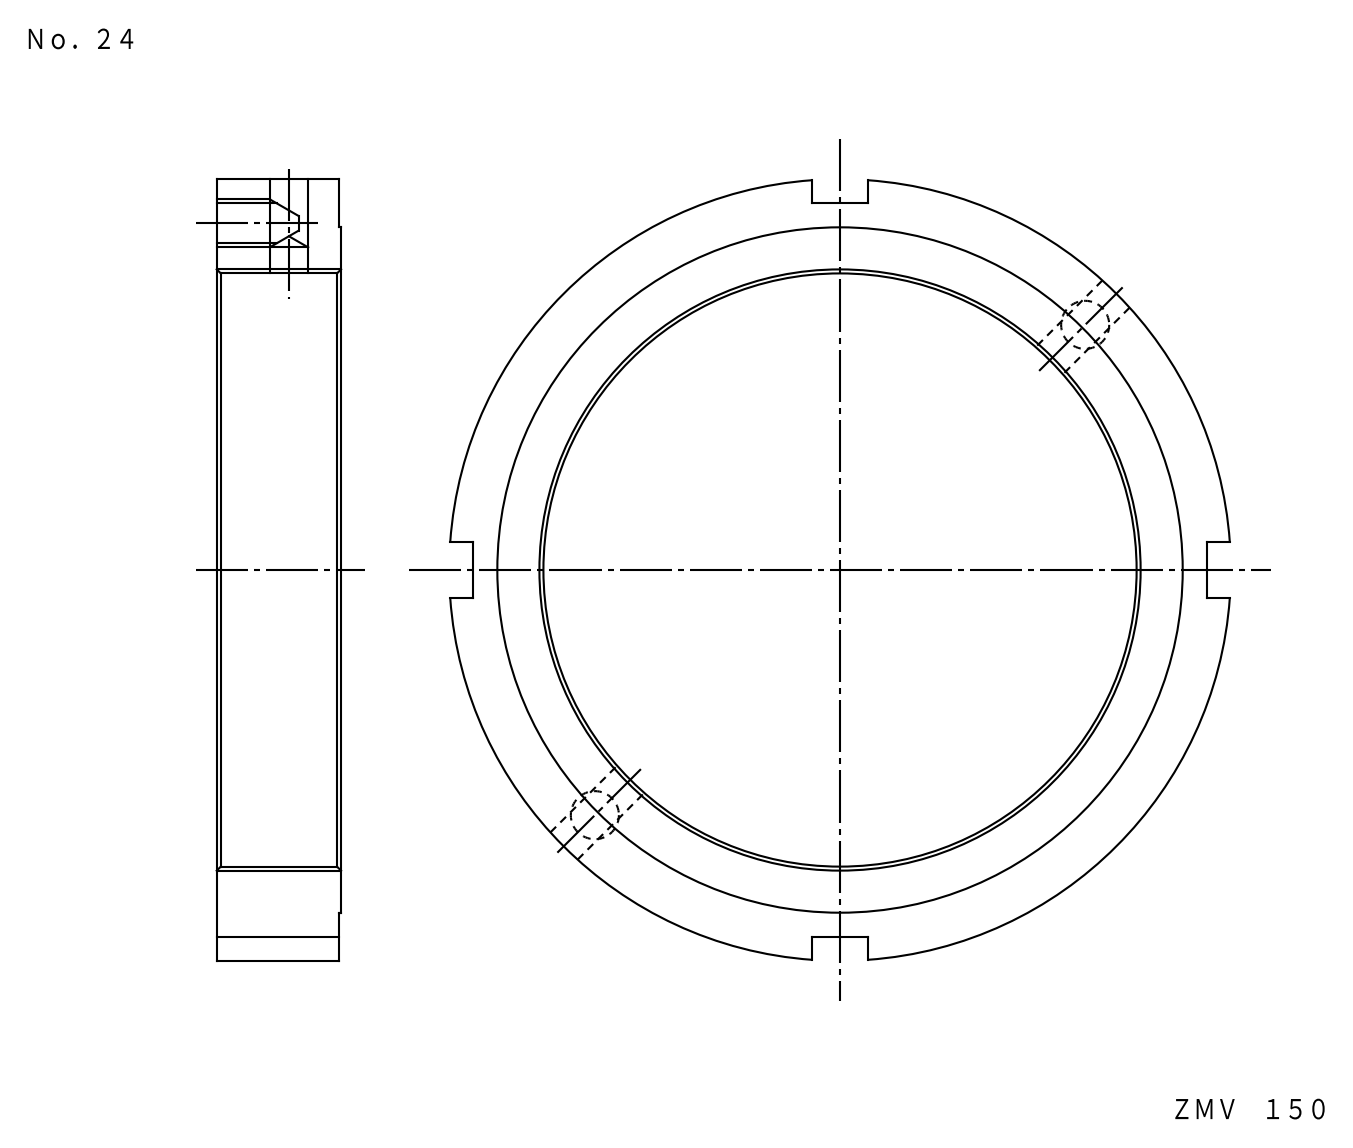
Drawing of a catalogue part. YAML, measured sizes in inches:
part_name: "FKD ZMV150"
step_written_by: "Autodesk Inventor LT (CONFIG_CONTROL_DESIGN)"
units: inches
bodies: {solids: 1, faces: 29, planar: 15, cylindrical: 10, other: 4}
overall_size: [7.657, 7.657, 1.22]
volume: 21.9
surface_area: 93.55
round_holes:
  - {diameter: 0.378, count: 2}
  - {diameter: 0.398, count: 2}
  - {diameter: 5.906, count: 1}
round_bosses_or_shafts:
  - {diameter: 7.677, count: 1}
  - {diameter: 6.732, count: 1}
face_to_face_distances: [1.201, 0.02, 1.22, 3.327, 3.878, 7.205, 0.551]
hole_center_spacings: [3.405, 6.811]
